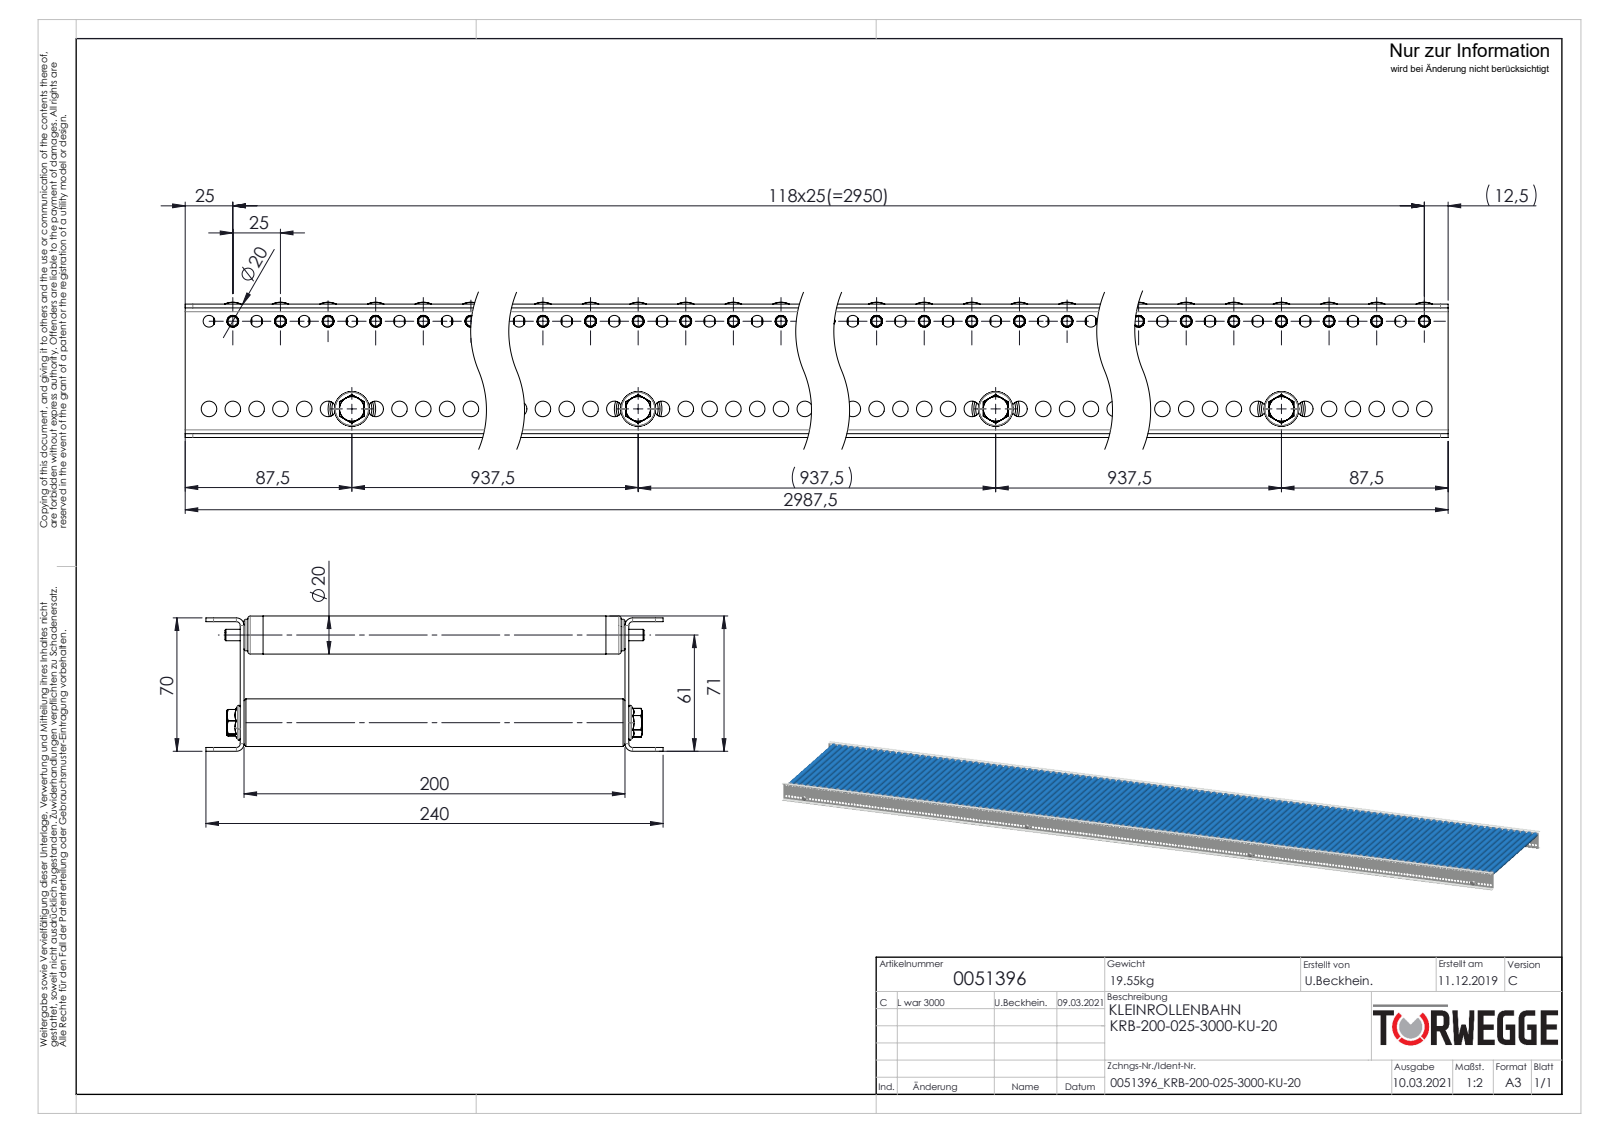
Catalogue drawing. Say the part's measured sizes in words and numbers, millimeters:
The part is named "0051396; KUT50-20x1,5-KU-A6_FA-EL=KFG_L=200; Traversen_KFG_L200; 0026257_TYP-KUT50-20X1,5-6 (+4 more)". Its 3-D file was written by "SolidWorks 2020 (AUTOMOTIVE_DESIGN)". It is 736 solids with 31448 faces: 10438 planar, 11758 cylindrical and 9252 other. Overall it measures 2987.5 by 240 by 71 millimeters. Its volume is 4 754 000 cubic millimeters and its surface area 5 394 000 square millimeters. Round holes: 238 of diameter 6.2, 238 of diameter 8.2, 119 of diameter 6.1, 119 of diameter 12.4, 119 of diameter 13.2, 119 of diameter 14.6, 119 of diameter 16.2, 119 of diameter 17, 119 of diameter 17.2, 4 of diameter 6.8, 4 of diameter 21. Round bosses or shafts: 119 of diameter 20, 119 of diameter 19.9, 119 of diameter 17.1, 119 of diameter 16.8, 119 of diameter 16.5, 119 of diameter 11.4, 119 of diameter 11.1, 119 of diameter 10.2. Partial cylindrical surfaces (rounded edges, fillets, slot ends): 119 of radius 4.05, 8 of radius 4, 4 of radius 2. The main face-to-face distances are 2, 202, 68, 200, 204, 70, 66, 192, 10, 12. The hole center spacings are 12.5, 25, 37.5, 50, 62.5, 75, 87.5, 100.
